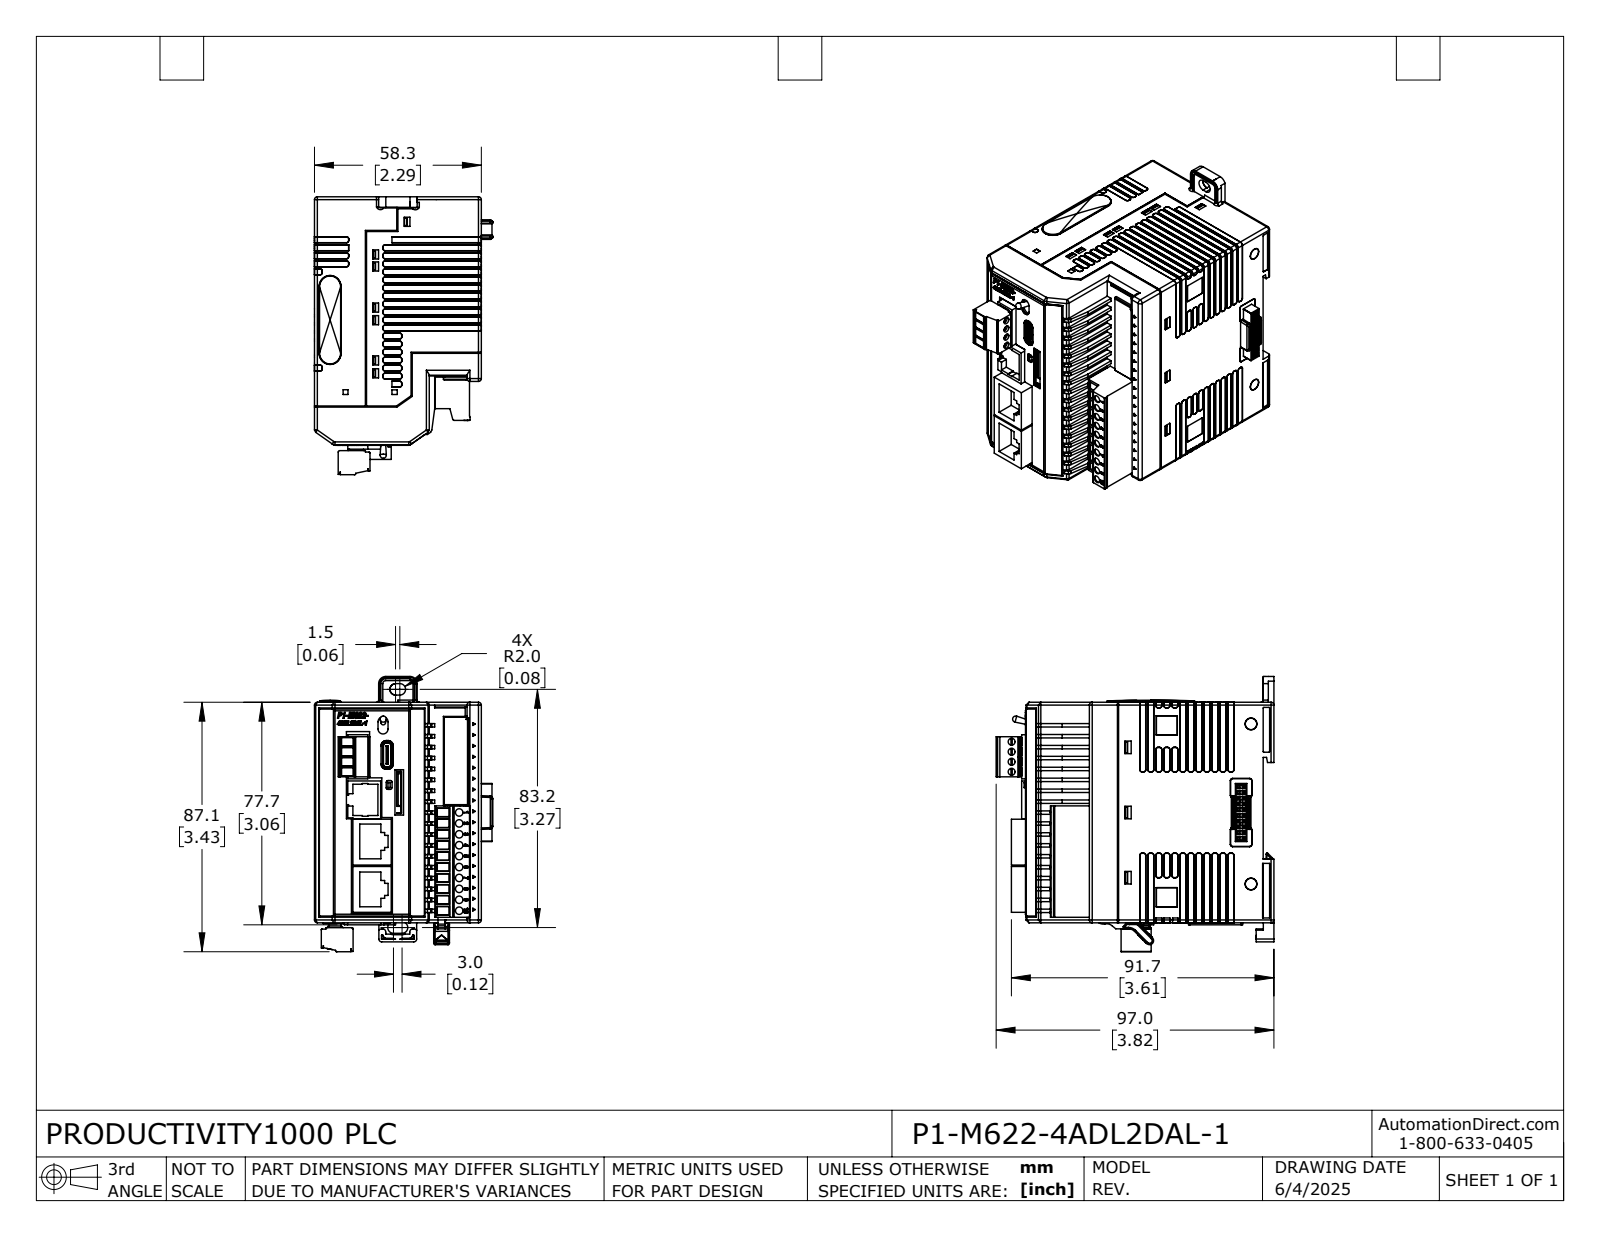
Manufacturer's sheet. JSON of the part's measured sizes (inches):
{"part_name": "P1-M622-4ADL2DAL-1", "step_written_by": "SolidWorks 2024 (AUTOMOTIVE_DESIGN)", "units": "inches", "bodies": {"solids": 15, "faces": 3845, "planar": 2231, "cylindrical": 892, "other": 722}, "overall_size": [3.686, 3.61, 2.452], "volume_in3": 2.186, "surface_area_in2": 120, "partial_cylinders_radius": [[0.01, 186], [0.008, 80], [0.02, 53], [0.039, 33], [0.079, 8], [0.024, 7], [0.059, 7], [0.012, 4]], "face_to_face_distances": [0.05, 0.02, 2.235, 0.039, 2.275, 3.01, 3.022, 2.294, 3.02, 3.031]}
